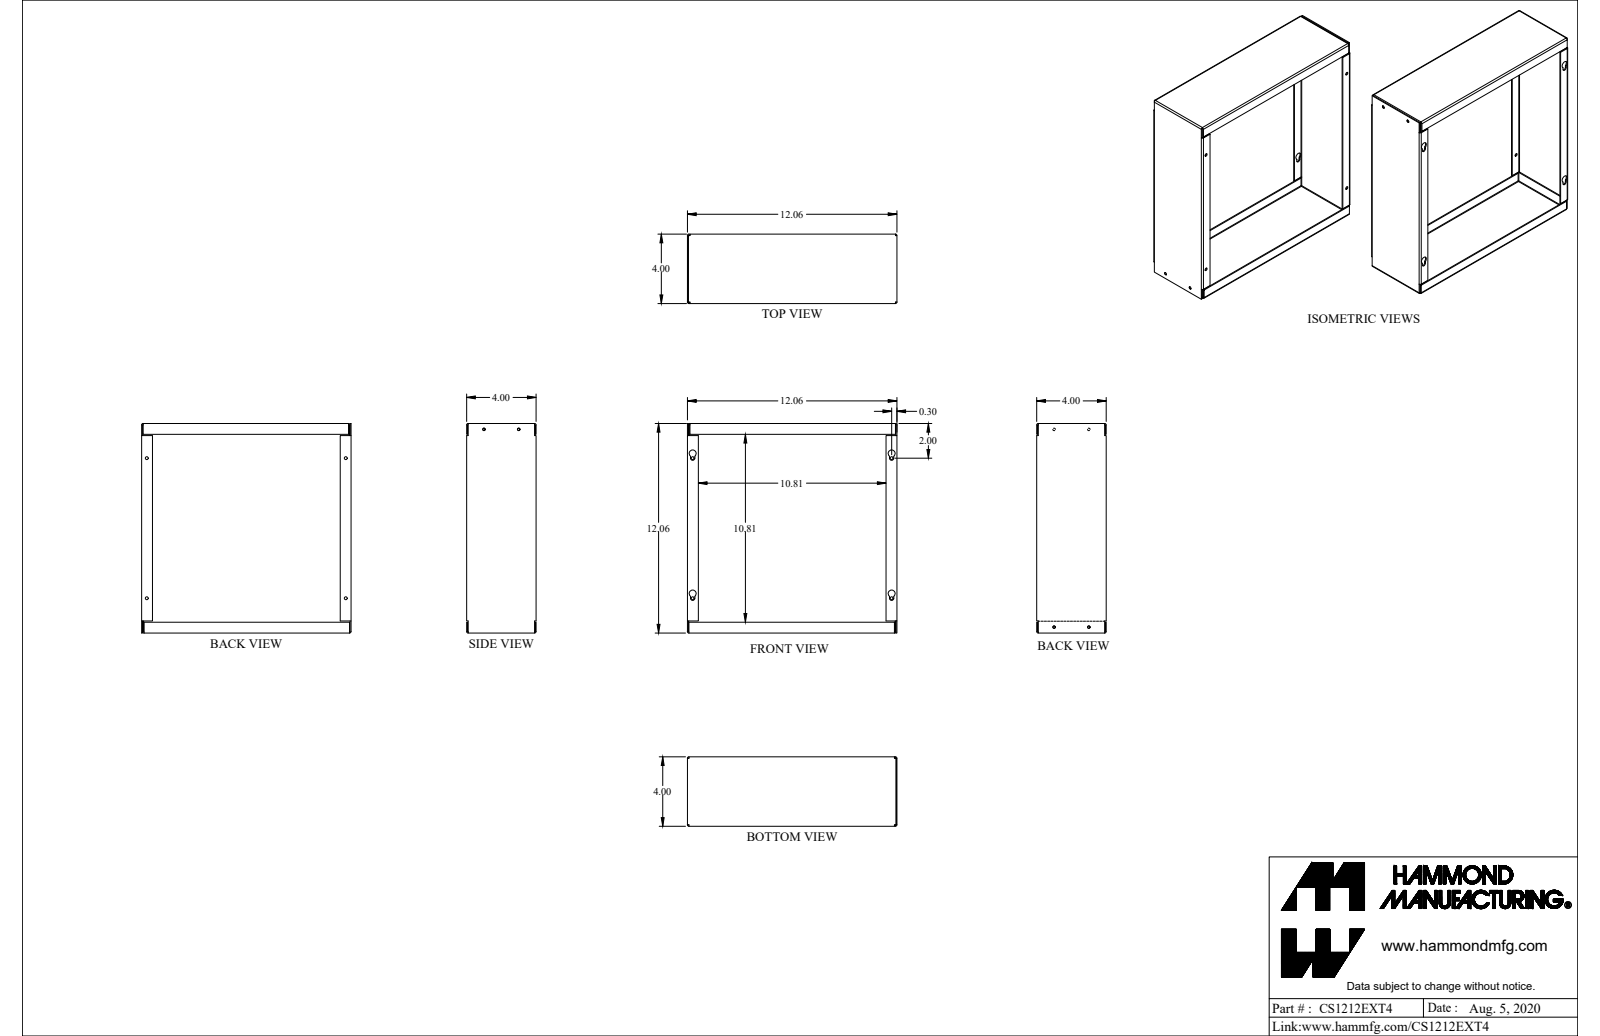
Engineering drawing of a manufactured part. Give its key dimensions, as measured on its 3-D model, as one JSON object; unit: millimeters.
{"part_name": "CS1212EXT4", "step_written_by": "SolidWorks 2021 (AUTOMOTIVE_DESIGN)", "units": "millimeters", "bodies": {"solids": 2, "faces": 124, "planar": 80, "cylindrical": 44, "other": 0}, "overall_size": [306.4, 306.4, 101.6], "volume_mm3": 227900, "surface_area_mm2": 319900, "round_holes": [[3.7, 4], [4.3, 4]], "round_bosses_or_shafts": [[3.3, 4]], "partial_cylinders_radius": [[0.7, 12], [2.2, 12], [3.2, 4], [5.2, 4]], "face_to_face_distances": [305, 1.4, 1.4, 303.5, 100.2, 306.4, 306.4, 303.5, 98.7, 101.6], "hole_center_spacings": [50.8, 204.8, 289.1, 291.1, 293.5, 355.9]}
